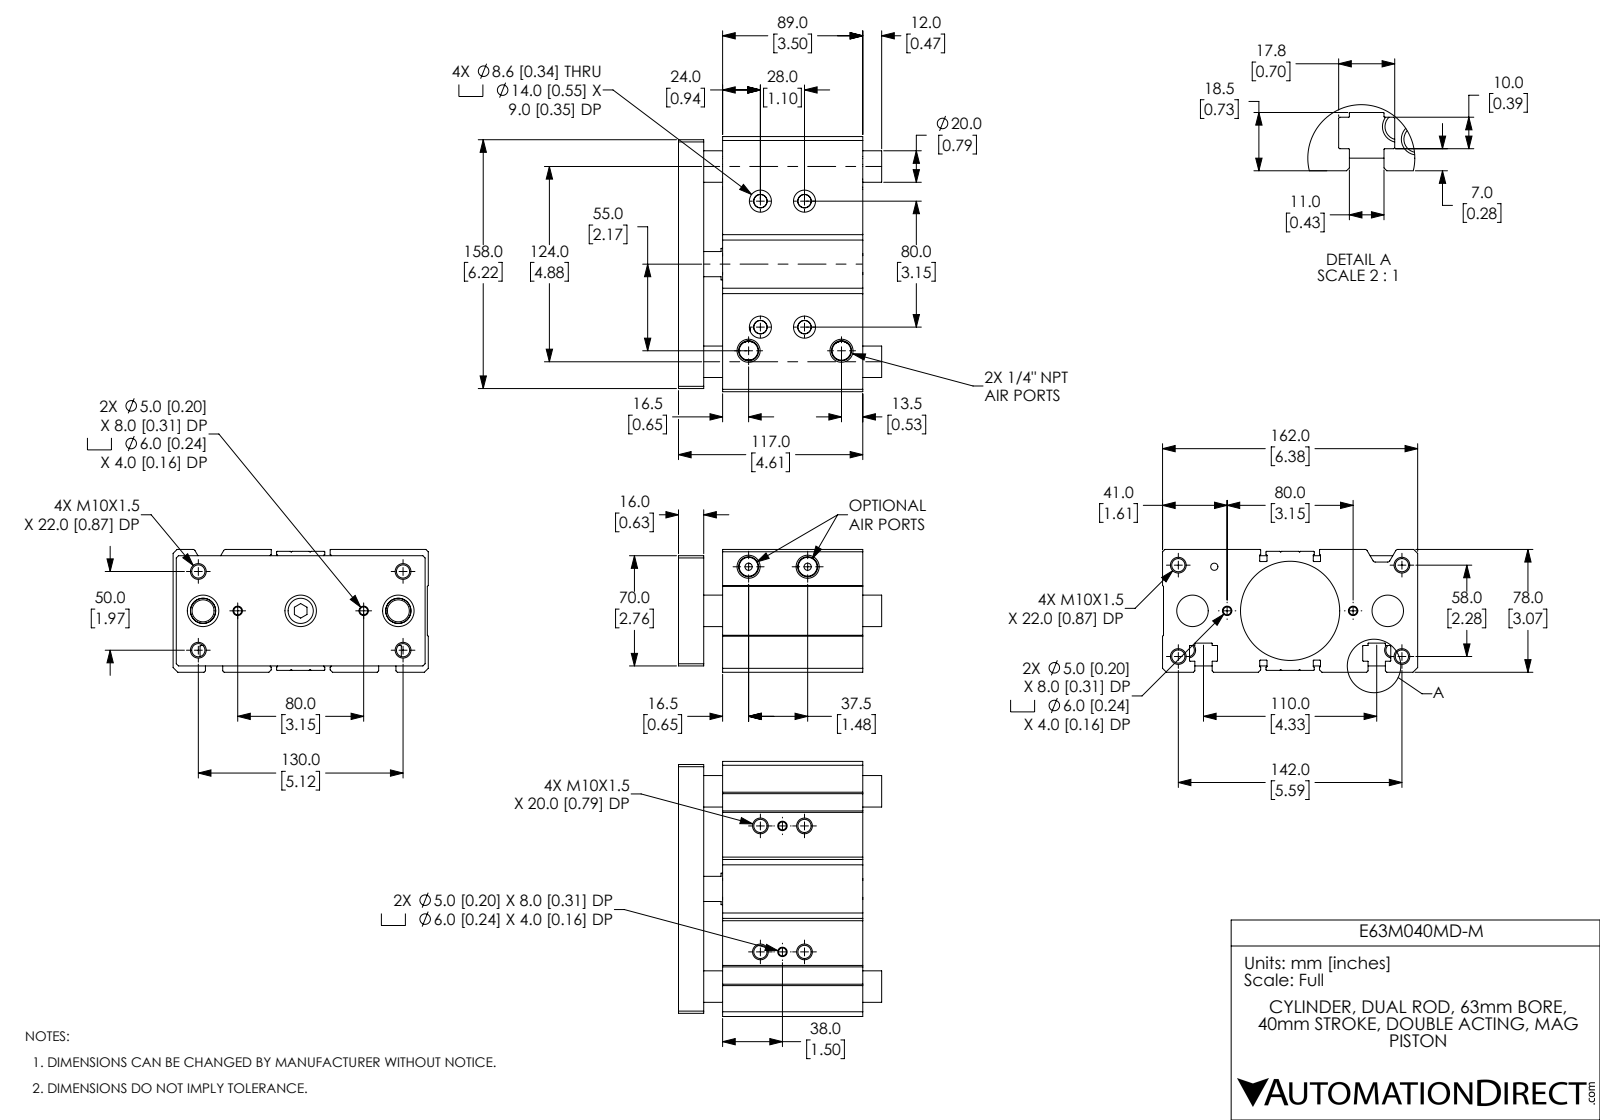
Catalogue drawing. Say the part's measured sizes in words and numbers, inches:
The part is named "E63M040MD-M_ENDPLATE; E63M040MD-M; E63M040MD-M_BODY". Its 3-D file was written by "SolidWorks 2019 (CONFIG_CONTROL_DESIGN)". It is 5 solids with 421 faces: 139 planar, 190 cylindrical and 92 other. Overall it measures 6.378 by 5.079 by 3.071 inches. Its volume is 66.03 cubic inches and its surface area 300.8 square inches. Round holes: 12 of diameter 0.33, 4 of diameter 0.197, 4 of diameter 0.236, 4 of diameter 0.339, 4 of diameter 0.551, 3 of diameter 0.18, 3 of diameter 0.394, 3 of diameter 0.787, 2 of diameter 0.63, 1 of diameter 0.787, 1 of diameter 2.48, 1 of diameter 2.48. Round bosses or shafts: 1 of diameter 0.63. Partial cylindrical surfaces (rounded edges, fillets, slot ends): 32 of radius 0.008, 28 of radius 0.016, 4 of radius 0.059, 2 of radius 0.012. The main face-to-face distances are 0.472, 1.102, 0.63, 3.976, 2.913, 3.071, 4.606, 3.504, 0.157, 4.341. The hole center spacings are 0.284, 0.551, 0.991, 1.195, 1.392, 1.671, 2.139, 2.742.
